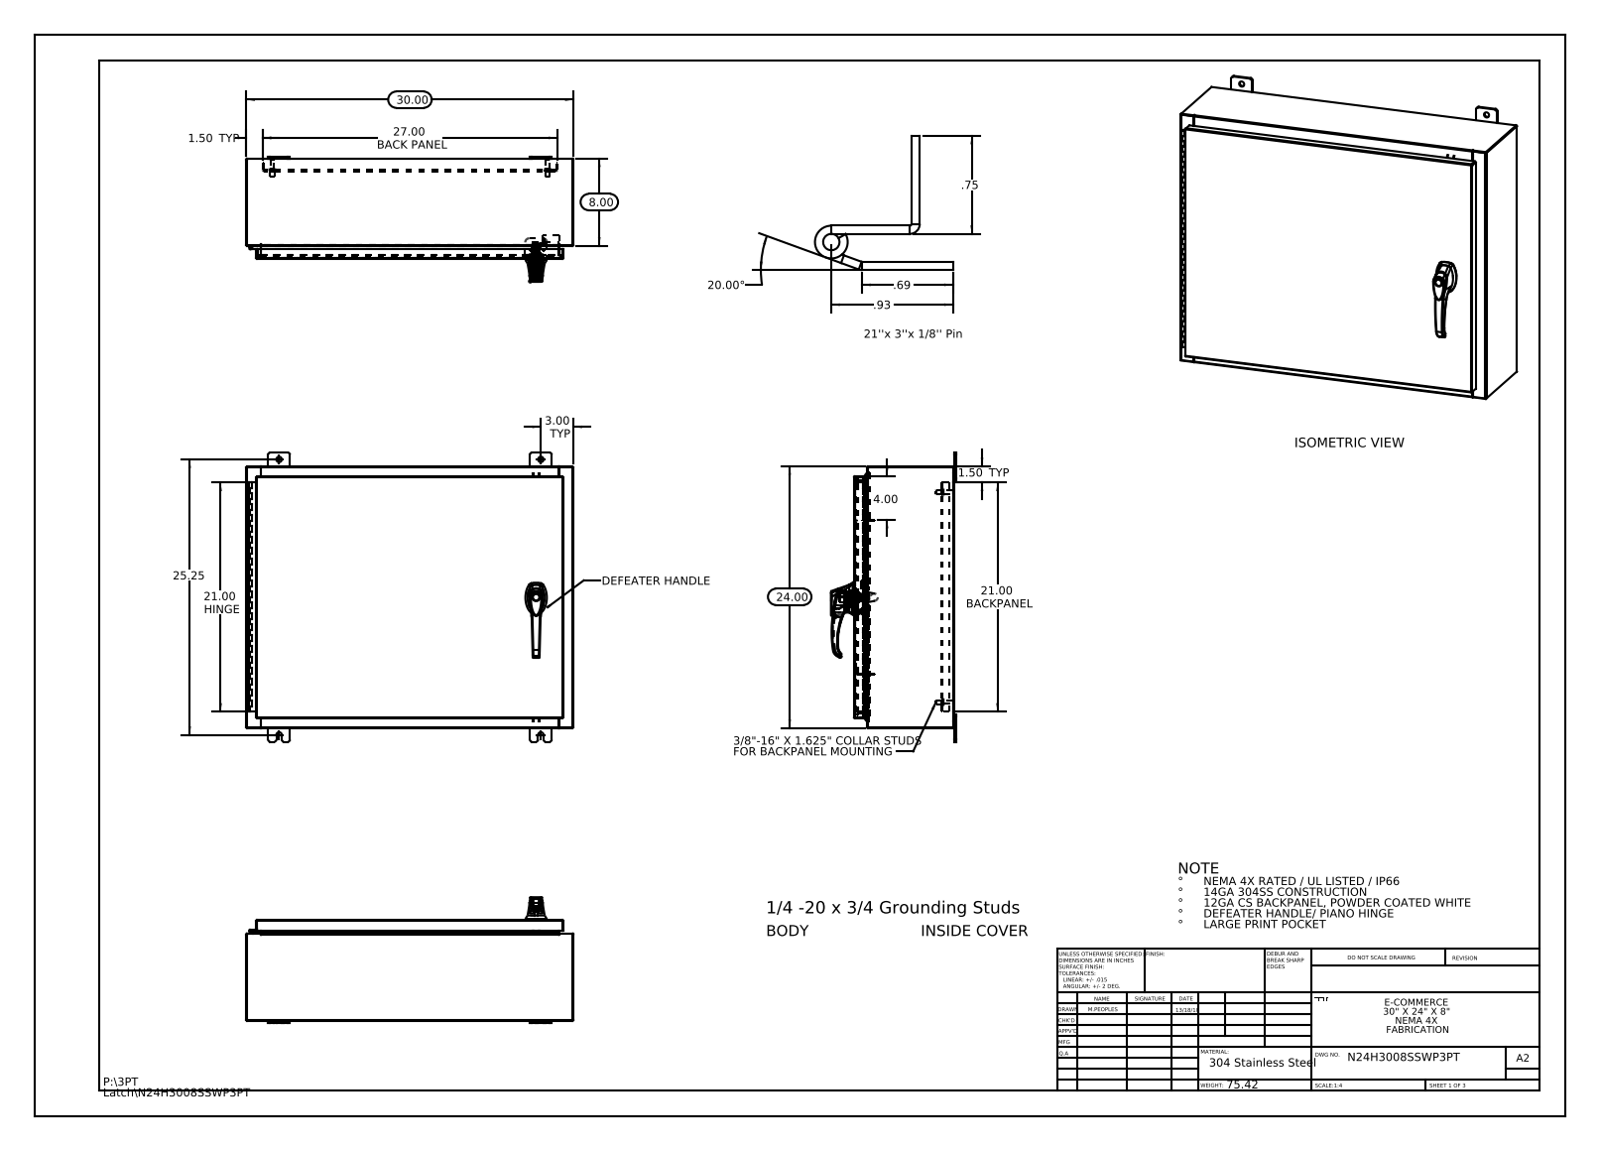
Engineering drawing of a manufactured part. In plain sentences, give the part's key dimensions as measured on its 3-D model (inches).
The part is named "21130102; g26103103_26163303; N24H3008SSWP3PT Defeater Handle - 3 - 2500-51 ZN; N24H3008SSWP3PT Defeater Handle Rod (+8 more)". Its 3-D file was written by "SolidWorks 2013 (CONFIG_CONTROL_DESIGN)". It is 31 solids with 2412 faces: 865 planar, 893 cylindrical and 654 other. Overall it measures 30 by 26.5 by 11.495 inches. Its volume is 267 cubic inches and its surface area 6 596 square inches. Round holes: 8 of diameter 0.5, 4 of diameter 0.25, 3 of diameter 0.138, 3 of diameter 0.161, 2 of diameter 0.079, 2 of diameter 0.203, 2 of diameter 0.313, 2 of diameter 0.437, 1 of diameter 0.125, 1 of diameter 0.125, 1 of diameter 0.197, 1 of diameter 0.276. Round bosses or shafts: 4 of diameter 0.625, 4 of diameter 0.375, 4 of diameter 0.33, 1 of diameter 1.181, 1 of diameter 0.748, 1 of diameter 0.68, 1 of diameter 0.661, 1 of diameter 0.639. Partial cylindrical surfaces (rounded edges, fillets, slot ends): 37 of radius 0.118, 33 of radius 0.006, 24 of radius 0.19, 22 of radius 0.013, 18 of radius 0.088, 15 of radius 0.039, 12 of radius 0.028, 6 of radius 0.008. The main face-to-face distances are 0.075, 9.126, 9.051, 9.201, 0.104, 1, 1.075, 8.051, 8.126, 1.179. The hole center spacings are 7.68, 24, 0.295, 0.625, 0.841, 1.25, 1.313, 1.561.
